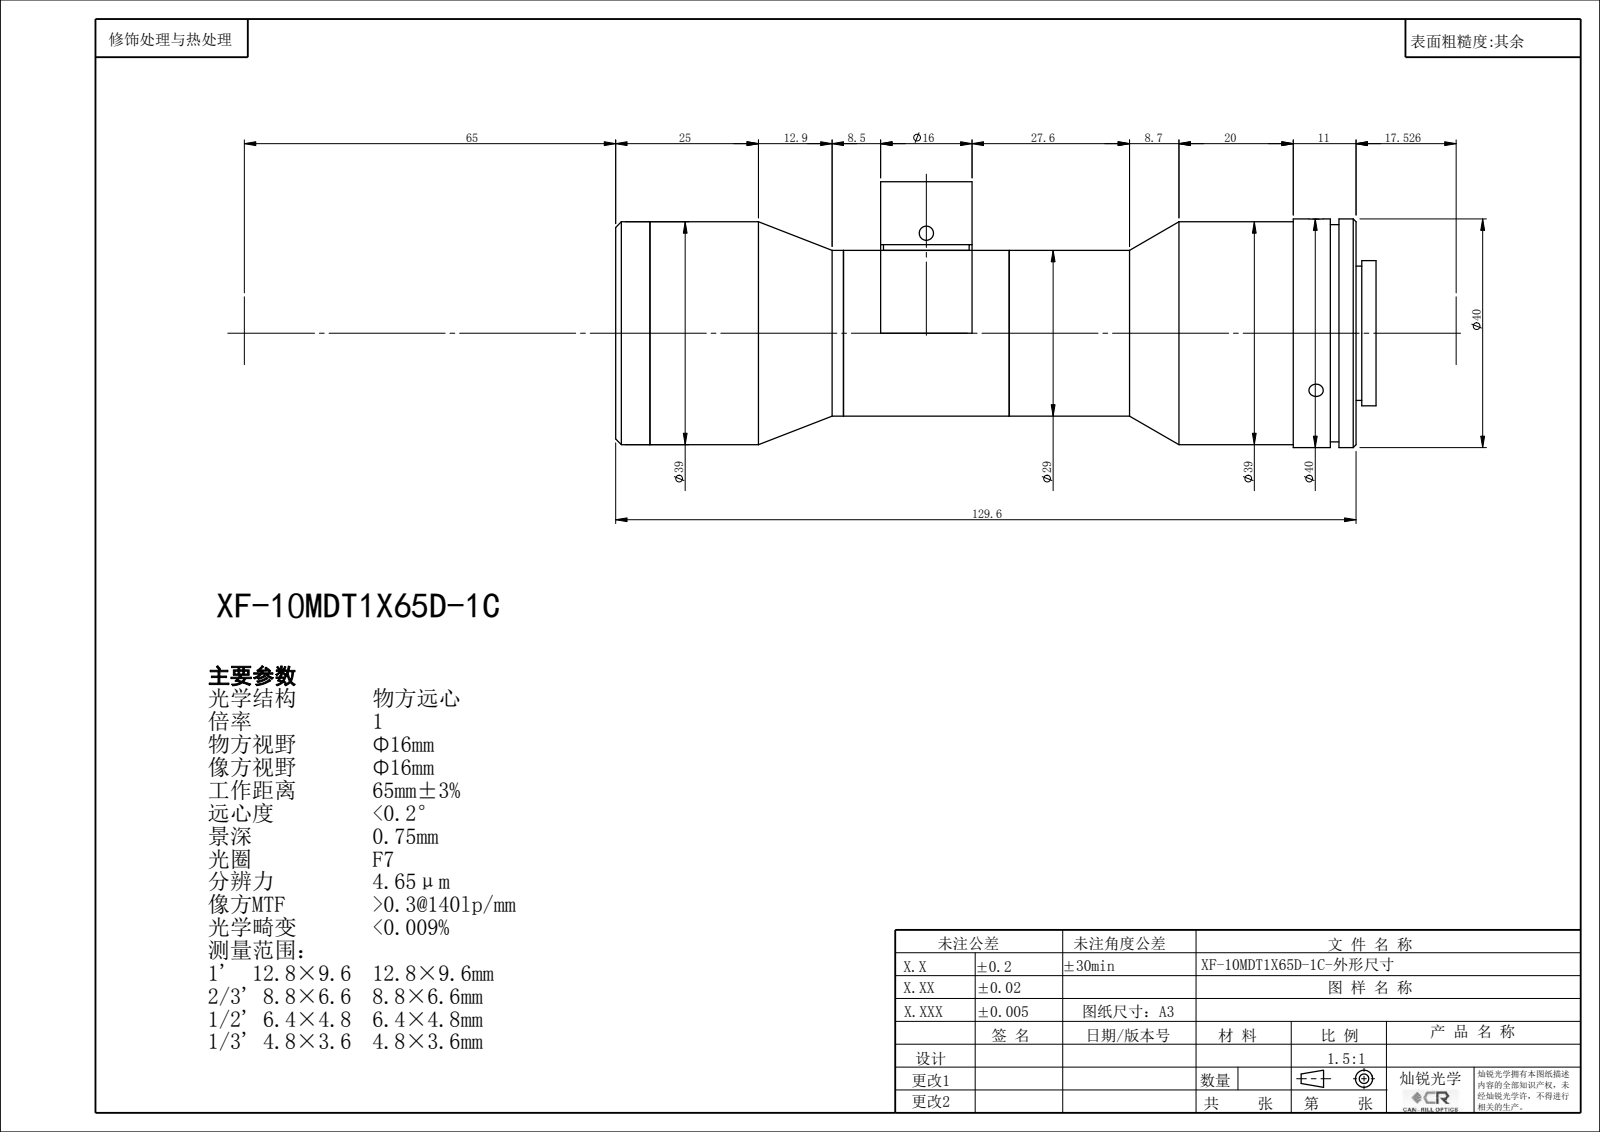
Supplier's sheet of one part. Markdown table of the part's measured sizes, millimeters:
| quantity | value |
| --- | --- |
| STEP written by | SolidWorks 2014 (CONFIG_CONTROL_DESIGN) |
| units | millimeters |
| bodies | 0 solids, 127 faces (46 planar, 67 cylindrical, 14 other) |
| overall size | 133.12 × 46.5 × 40 |
| round holes (diameter × count) | 1.6 × 4, 2.2 × 4, 2.5 × 4, 8 × 1, 14 × 1, 16 × 1, 21.4 × 1, 24.4 × 1, 31 × 1, 32.4 × 1, 35 × 1 |
| round bosses / shafts (diameter × count) | 40 × 1, 39 × 1, 38 × 1, 29 × 1, 25.4 × 1, 23.5 × 1, 16 × 1 |
| main face-to-face distances | 11, 6.5, 123.62, 112.62, 29, 1, 129.62, 118.62, 6, 8 |
| hole center spacings | 11.66, 12, 20, 23.32, 63.03, 74.9, 68.23 |
